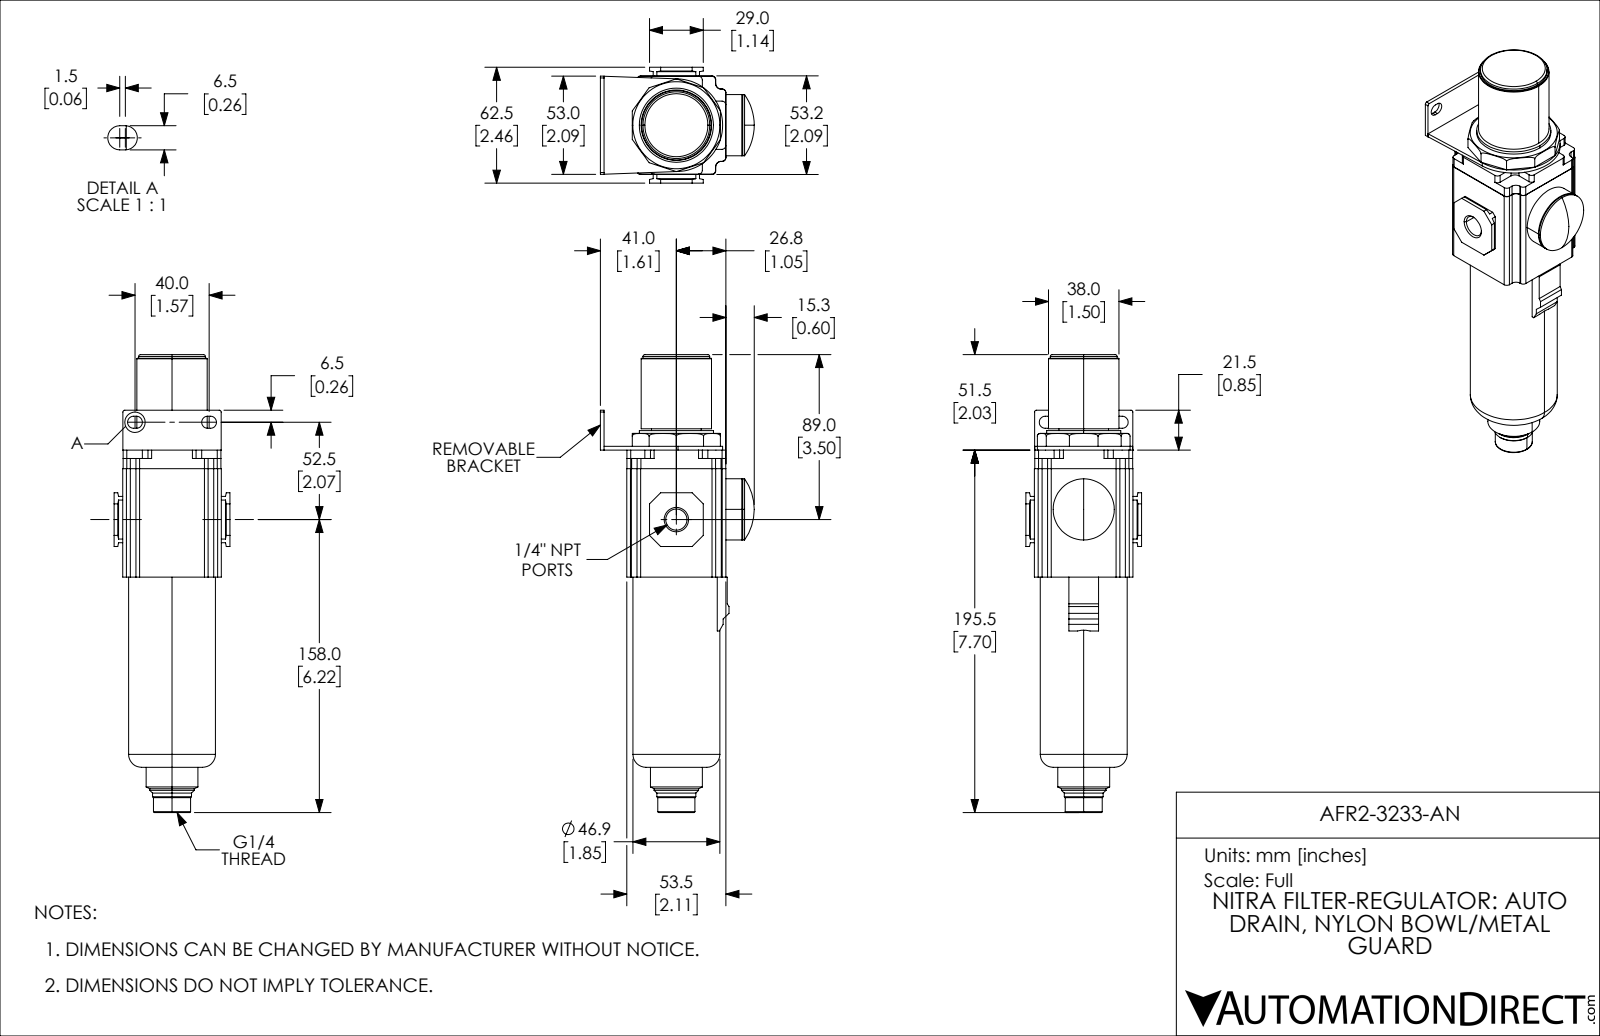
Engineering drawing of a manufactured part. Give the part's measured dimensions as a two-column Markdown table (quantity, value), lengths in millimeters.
| quantity | value |
| --- | --- |
| part name | AFR2-3233-AN |
| STEP written by | SolidWorks 2019 (CONFIG_CONTROL_DESIGN) |
| units | millimeters |
| bodies | 1 solid, 221 faces (124 planar, 71 cylindrical, 26 other) |
| overall size | 247 × 83.03 × 62.5 |
| volume | 452 721 mm³ |
| surface area | 51 631 mm² |
| round holes (diameter × count) | 11.45 × 2 |
| round bosses / shafts (diameter × count) | 46.9 × 1, 40 × 1, 38 × 1, 36 × 1, 33 × 1, 28 × 1, 26.78 × 1, 24 × 1 |
| partial cylindrical surfaces (radius × count) | 2 × 24, 3 × 12, 3.25 × 4, 1 × 2, 25 × 1 |
| main face-to-face distances | 2, 53.2, 53.5, 4.65, 57.85, 14.25, 12.25, 67.75, 51.5, 49.5 |
